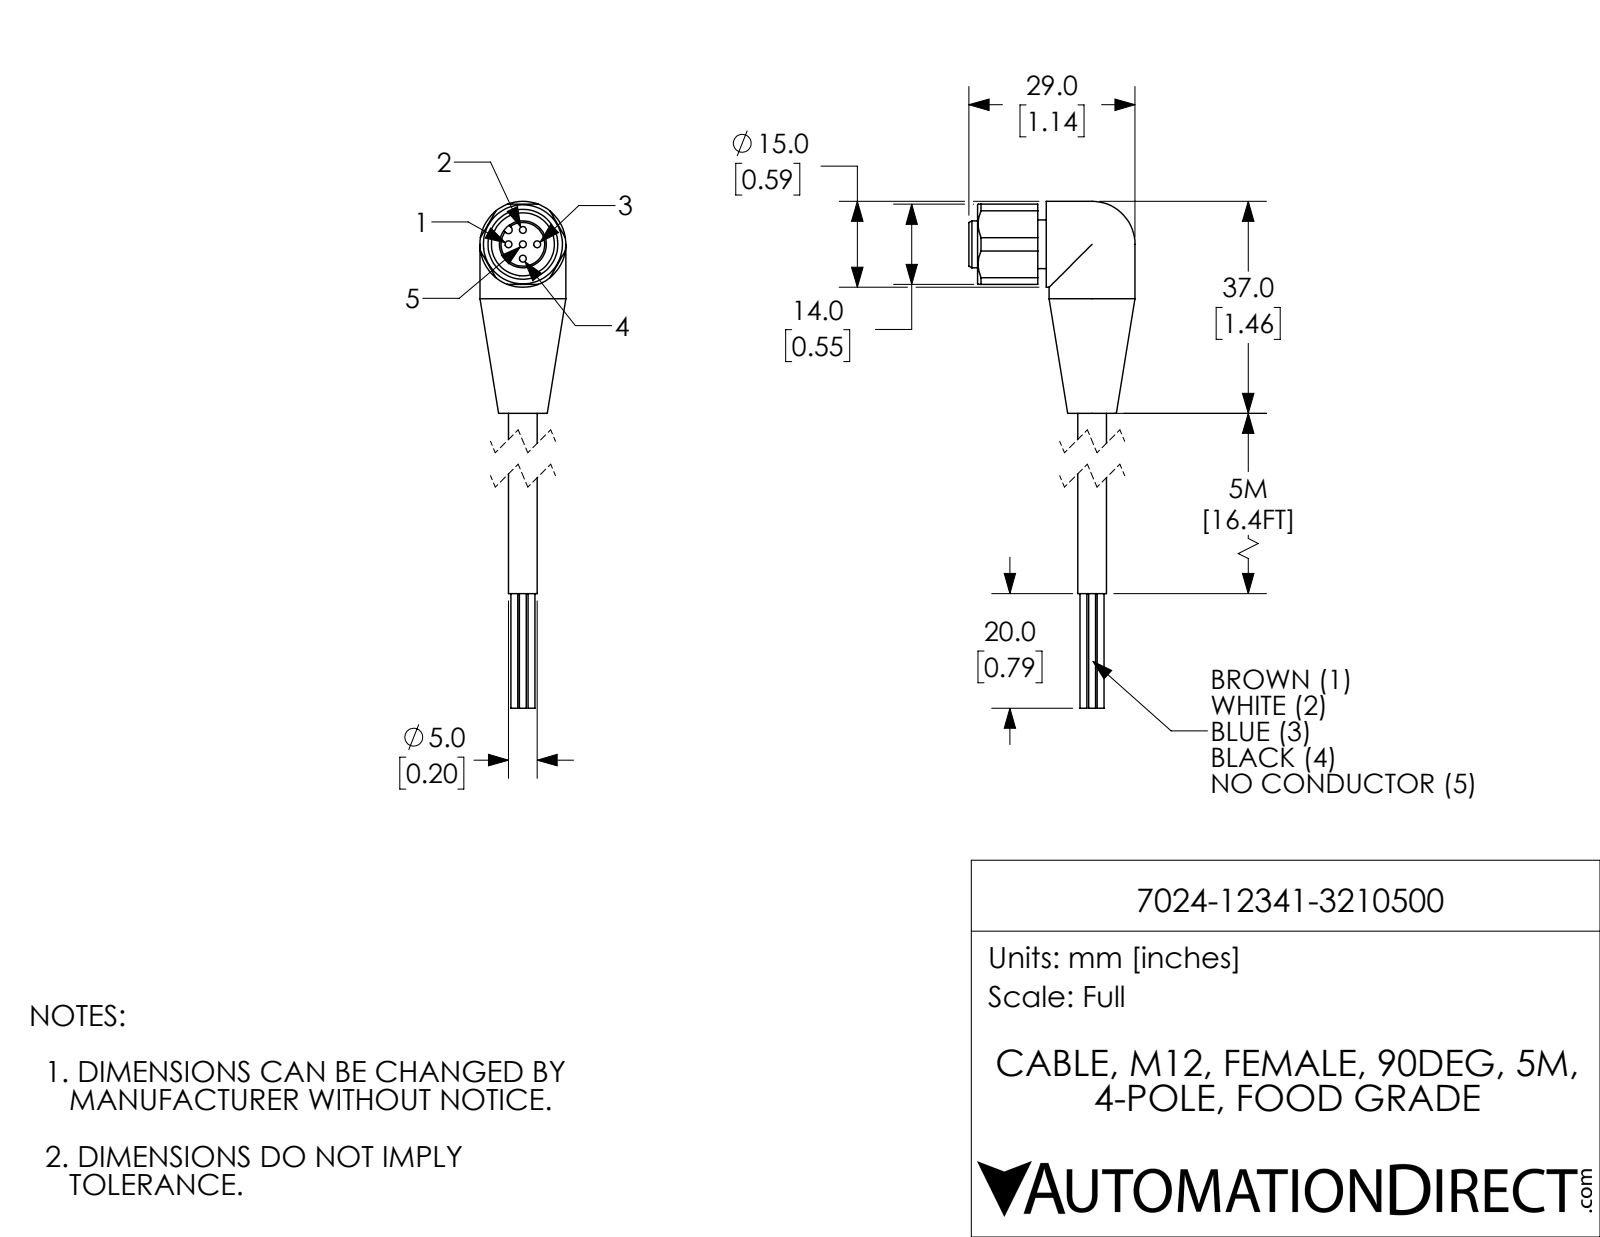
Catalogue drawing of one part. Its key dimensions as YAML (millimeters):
part_name: "7024-12341-3210500"
step_written_by: "SolidWorks 2018 (AUTOMOTIVE_DESIGN)"
units: millimeters
bodies: {solids: 1, faces: 73, planar: 25, cylindrical: 38, other: 10}
overall_size: [87, 29, 15]
volume: 7402
surface_area: 3886
round_holes:
  - {diameter: 1.2, count: 5}
  - {diameter: 11, count: 1}
round_bosses_or_shafts:
  - {diameter: 1.2, count: 4}
  - {diameter: 15, count: 2}
  - {diameter: 8.5, count: 1}
  - {diameter: 8.2, count: 1}
  - {diameter: 5, count: 1}
partial_cylinders:
  - {radius: 0.65, count: 1}
face_to_face_distances: [14, 1.5, 12, 4.5, 3, 13.5, 9, 22.5, 36.5, 10.5]
hole_center_spacings: [2.5, 3.54, 5]
